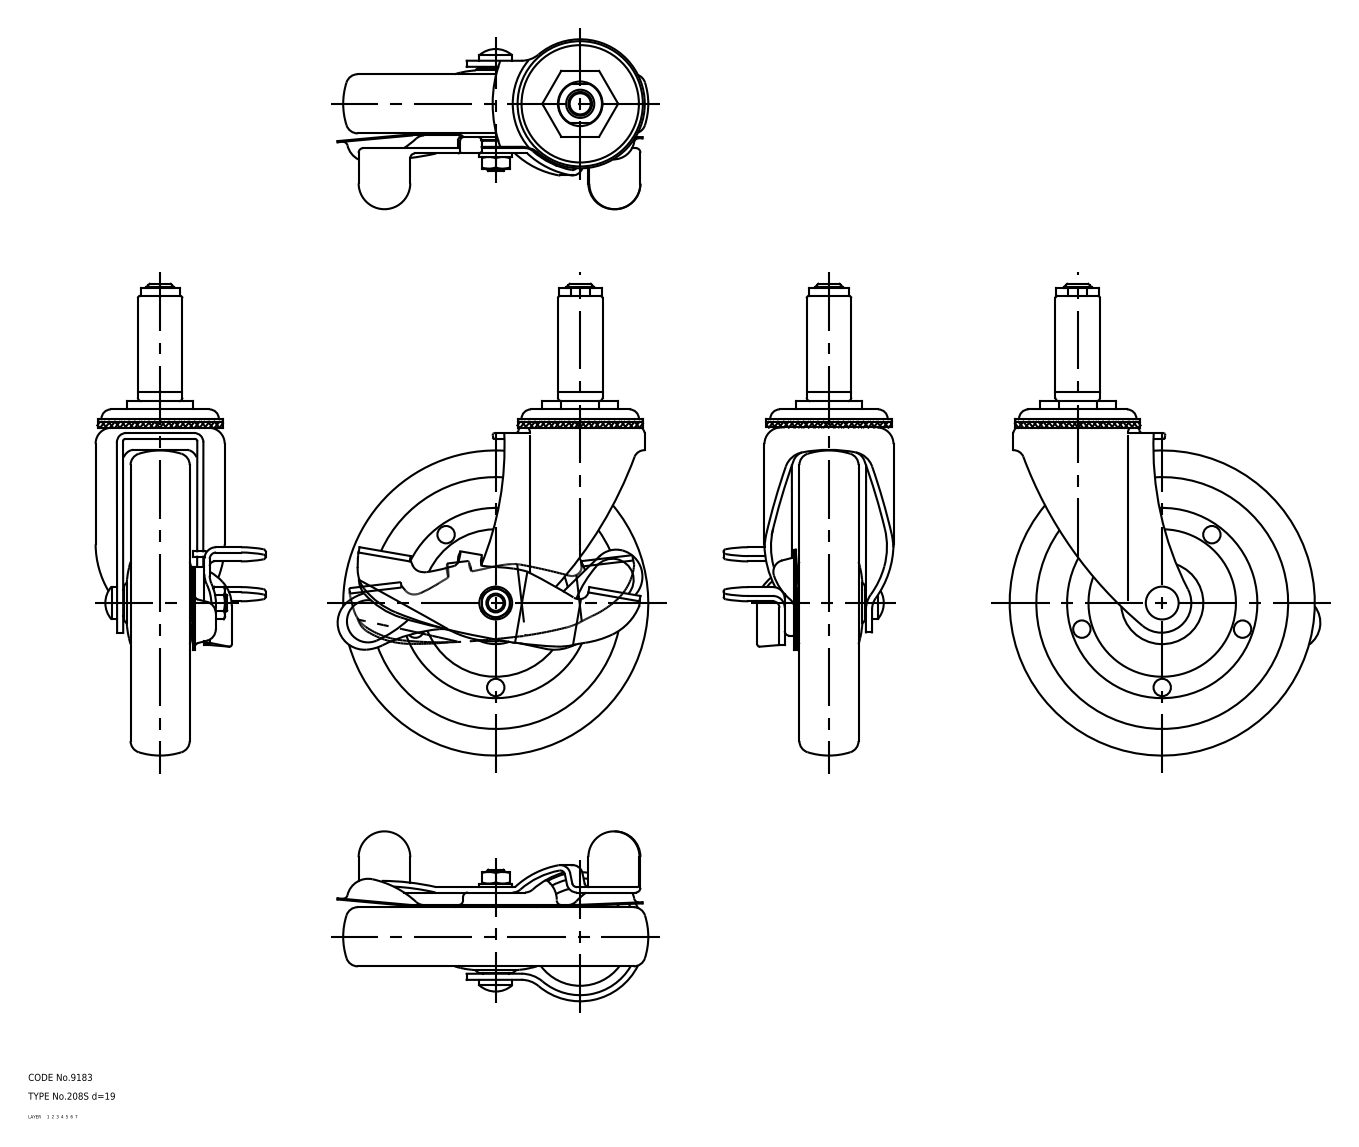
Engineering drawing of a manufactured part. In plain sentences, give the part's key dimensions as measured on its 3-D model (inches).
The part is named "lever; wheel; plate; main shaft (+2 more)". Its 3-D file was written by "CADfix (AUTOMOTIVE_DESIGN)". It is 6 solids with 398 faces: 0 planar, 0 cylindrical and 398 other. Overall it measures 7.913 by 5.211 by 2.851 inches. Its volume is 19.47 cubic inches and its surface area 136.1 square inches.
